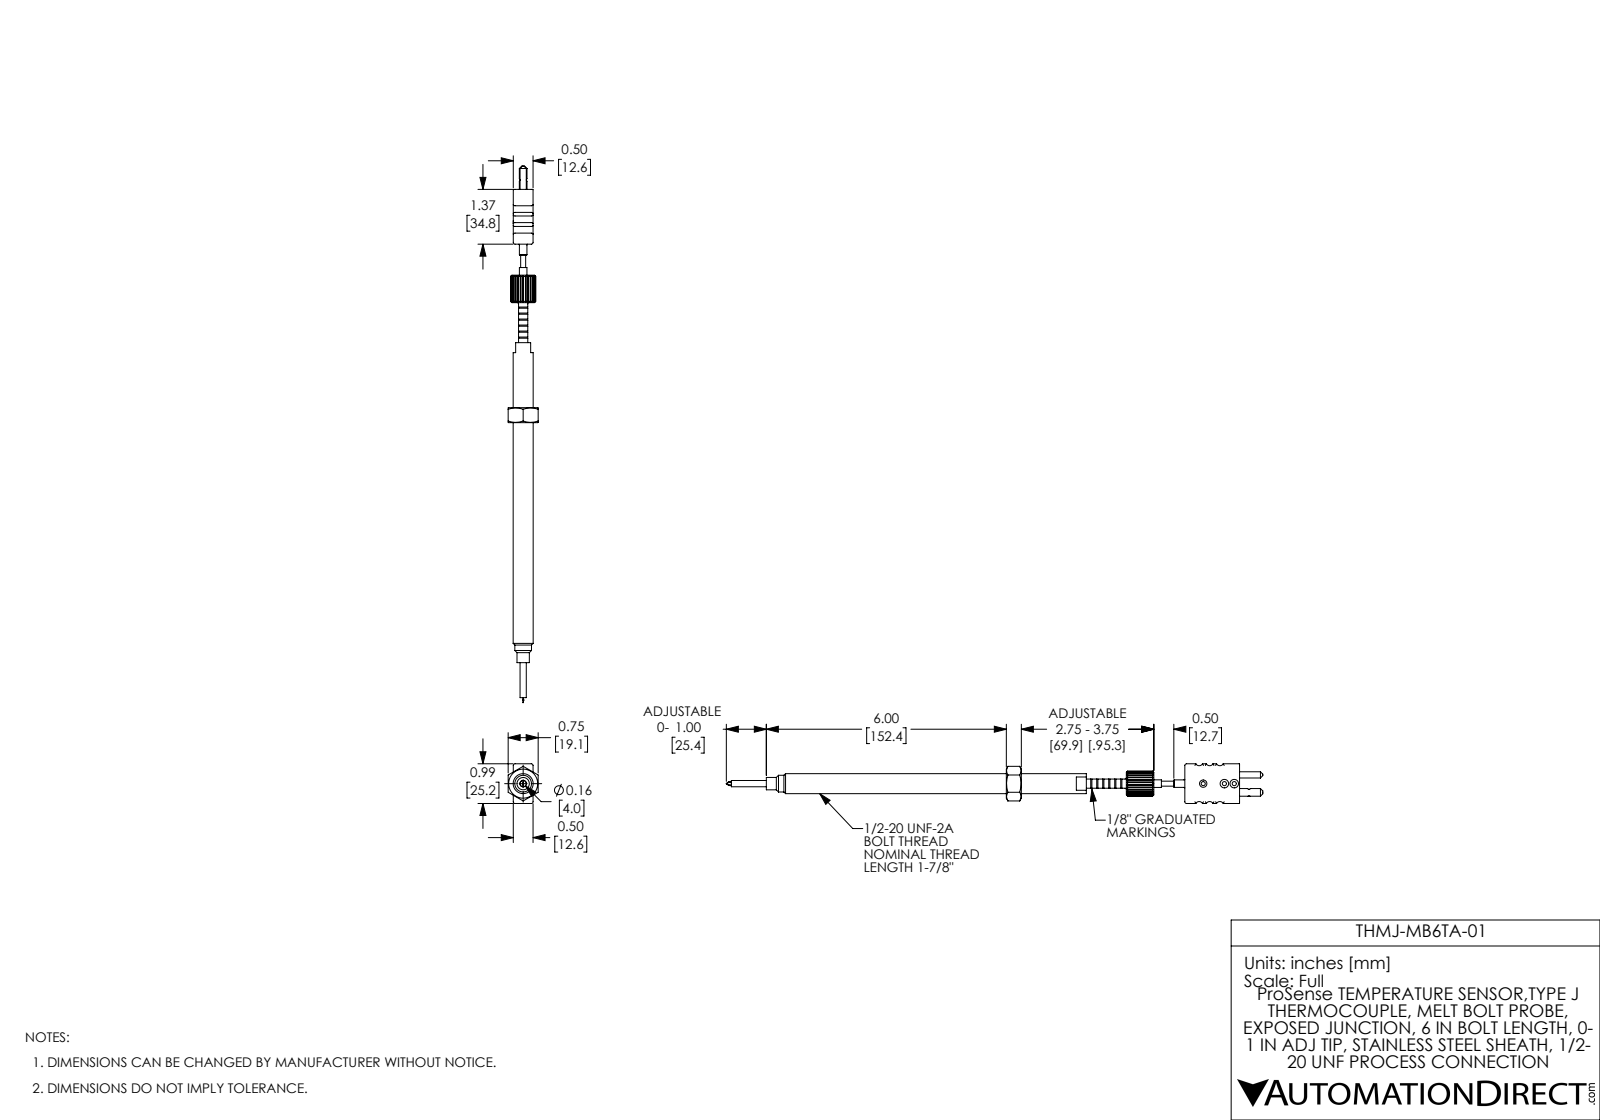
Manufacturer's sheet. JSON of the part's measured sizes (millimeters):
{"part_name": "THMJ-MB6TA-01", "step_written_by": "SolidWorks 2017 (AUTOMOTIVE_DESIGN)", "units": "millimeters", "bodies": {"solids": 4, "faces": 372, "planar": 145, "cylindrical": 125, "other": 102}, "overall_size": [340.7, 25.2, 19.1], "volume_mm3": 42100, "surface_area_mm2": 16050, "round_holes": [[2.6, 2], [4, 2], [3.2, 1], [4.2, 1], [4.7, 1], [7.5, 1], [7.8, 1]], "round_bosses_or_shafts": [[4, 2], [0.4, 2], [12.7, 1], [10.6, 1], [7.9, 1], [7.8, 1], [7.1, 1], [5.8, 1]], "partial_cylinders_radius": [[1.1, 8], [2.4, 6], [0.3, 4], [8, 1]], "face_to_face_distances": [12.6, 19.1, 25.2, 7.6, 9.5, 3.2, 15.8, 34.8, 25.4, 42.9], "hole_center_spacings": [5.5, 8.4, 14.5, 6.3, 11, 13.4, 19.7]}
